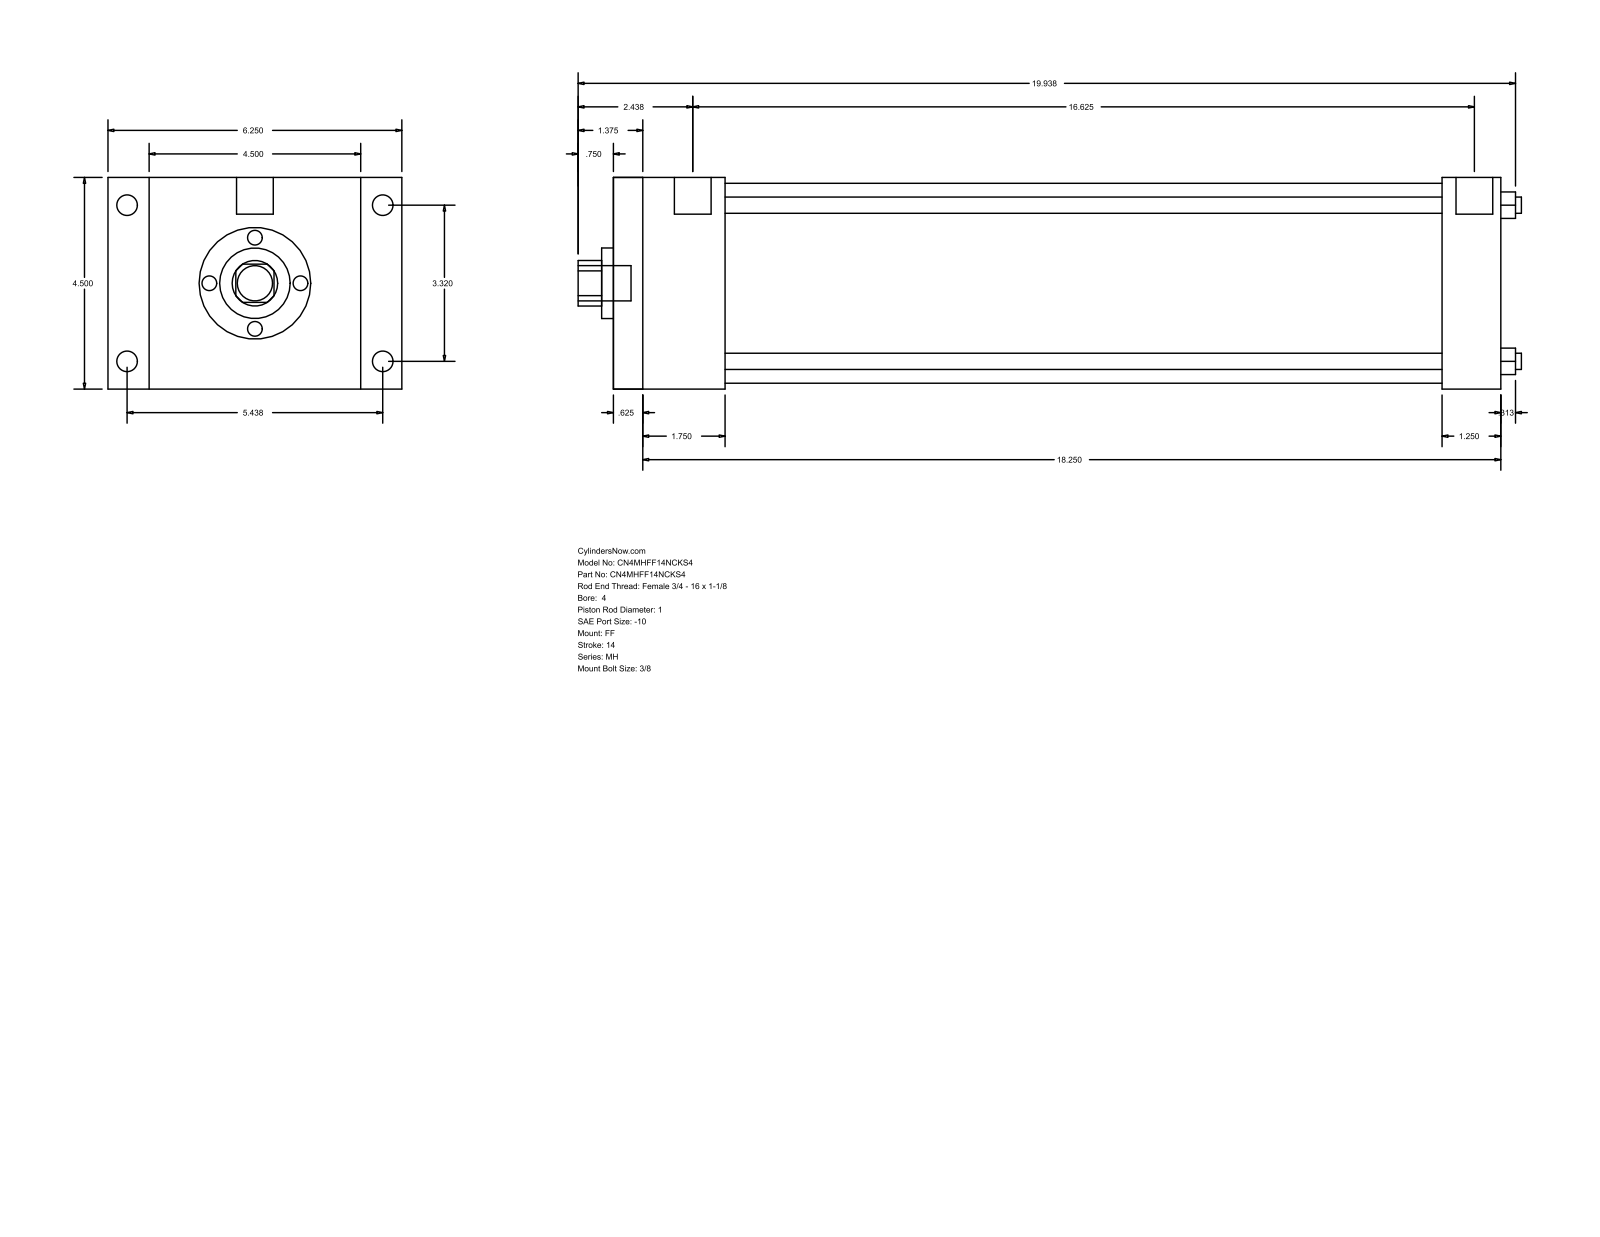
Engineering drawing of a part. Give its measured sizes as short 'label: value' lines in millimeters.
name: MH_FF__0400_1
written by: GSSL Pune (CONFIG_CONTROL_DESIGN)
unit: mm
bodies: 0 solids, 92 faces (64 planar, 28 cylindrical, 0 other)
size: 509.59 × 158.75 × 114.3
holes: 4× ⌀8.76, 1× ⌀25.4, 1× ⌀38.1, 1× ⌀107.95
bosses: 4× ⌀11.13, 4× ⌀8.73, 2× ⌀19.84, 1× ⌀19.05
rounds: 1× R12.29
face distances: 114.3, 479.43, 15.87, 463.56, 60.33, 44.46, 419.1, 447.68, 431.81, 387.35
hole spacings: 59.62, 84.32, 119.25
